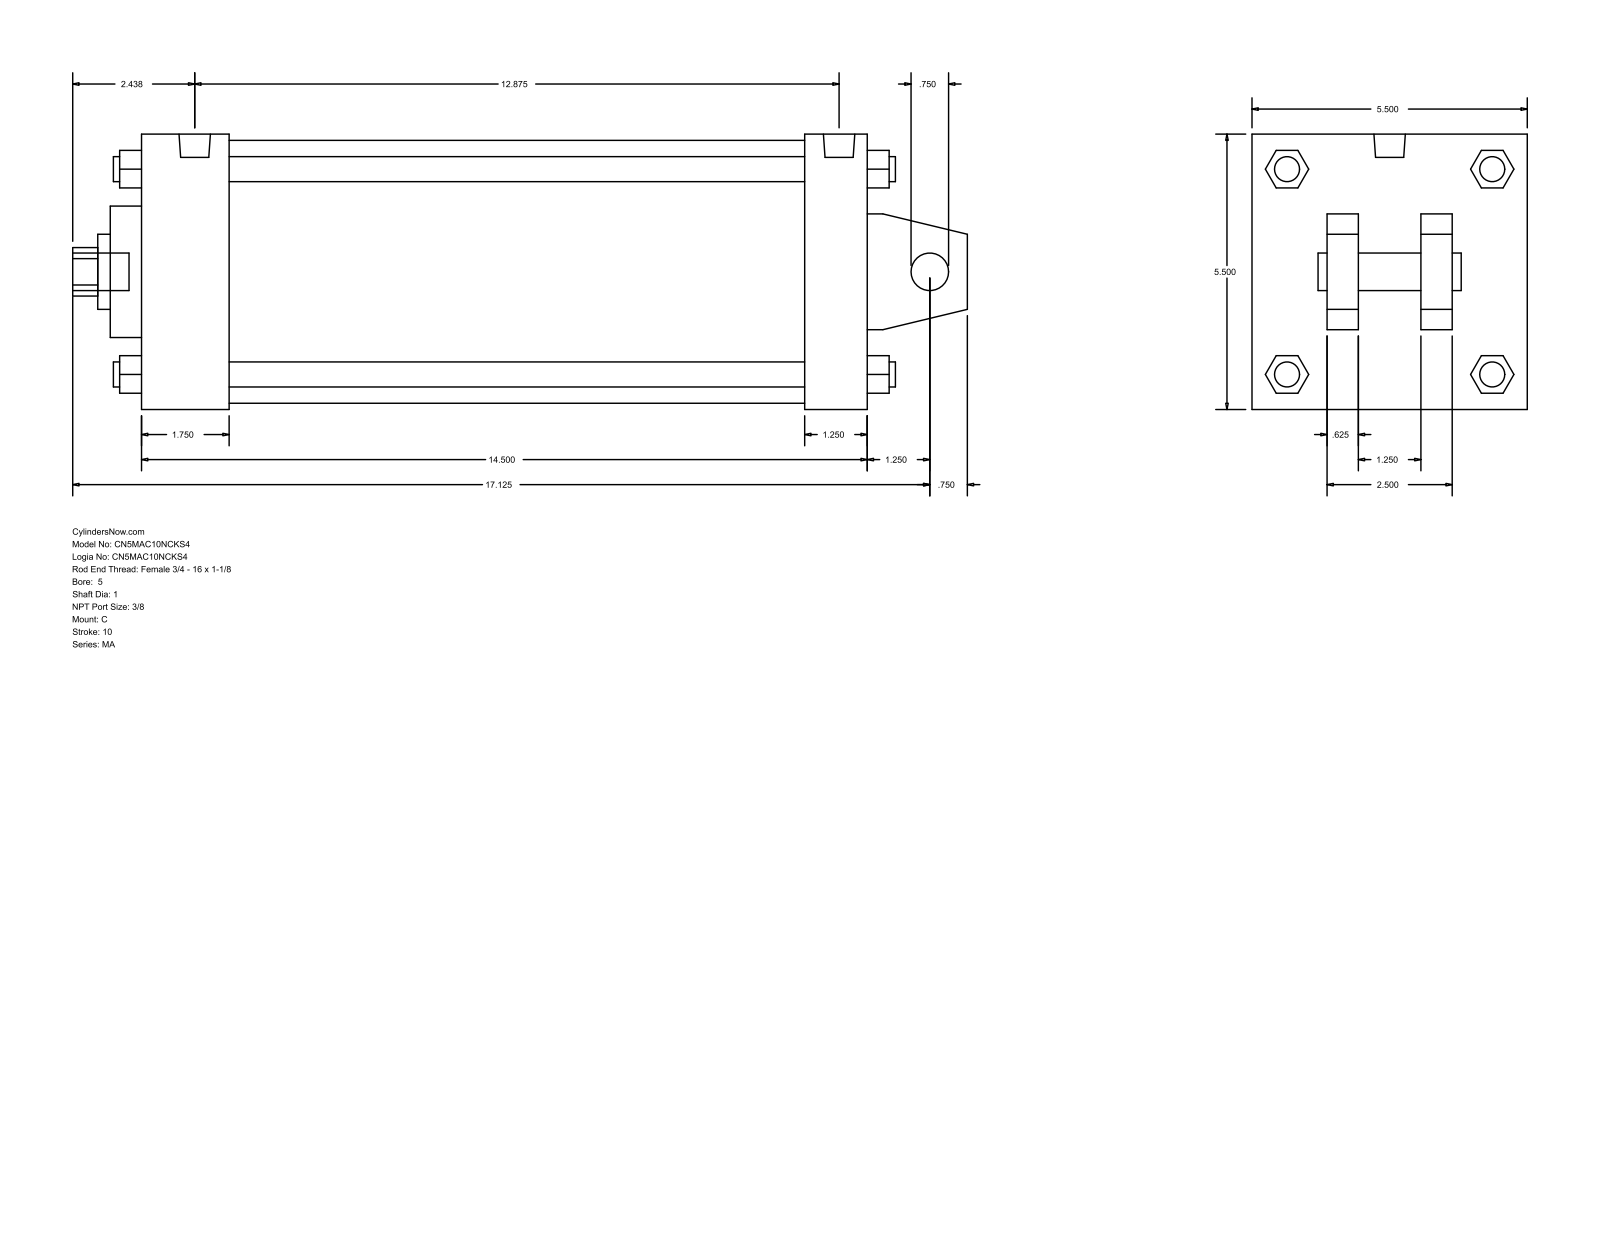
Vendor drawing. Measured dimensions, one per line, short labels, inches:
name: MA_C__0500_1
written by: GSSL Pune (CONFIG_CONTROL_DESIGN)
unit: in
bodies: 0 solids, 141 faces (109 planar, 32 cylindrical, 0 other)
size: 17.875 × 5.5 × 5.5
holes: 1× ⌀0.75, 1× ⌀1, 1× ⌀1.5, 1× ⌀2.625, 1× ⌀5.25
bosses: 4× ⌀0.5, 4× ⌀0.437, 2× ⌀0.627, 1× ⌀0.75
rounds: 1× R0.484
face distances: 5.5, 14.5, 0.625, 13.25, 1.25, 1.75, 11.5, 12.75, 1.5, 4
